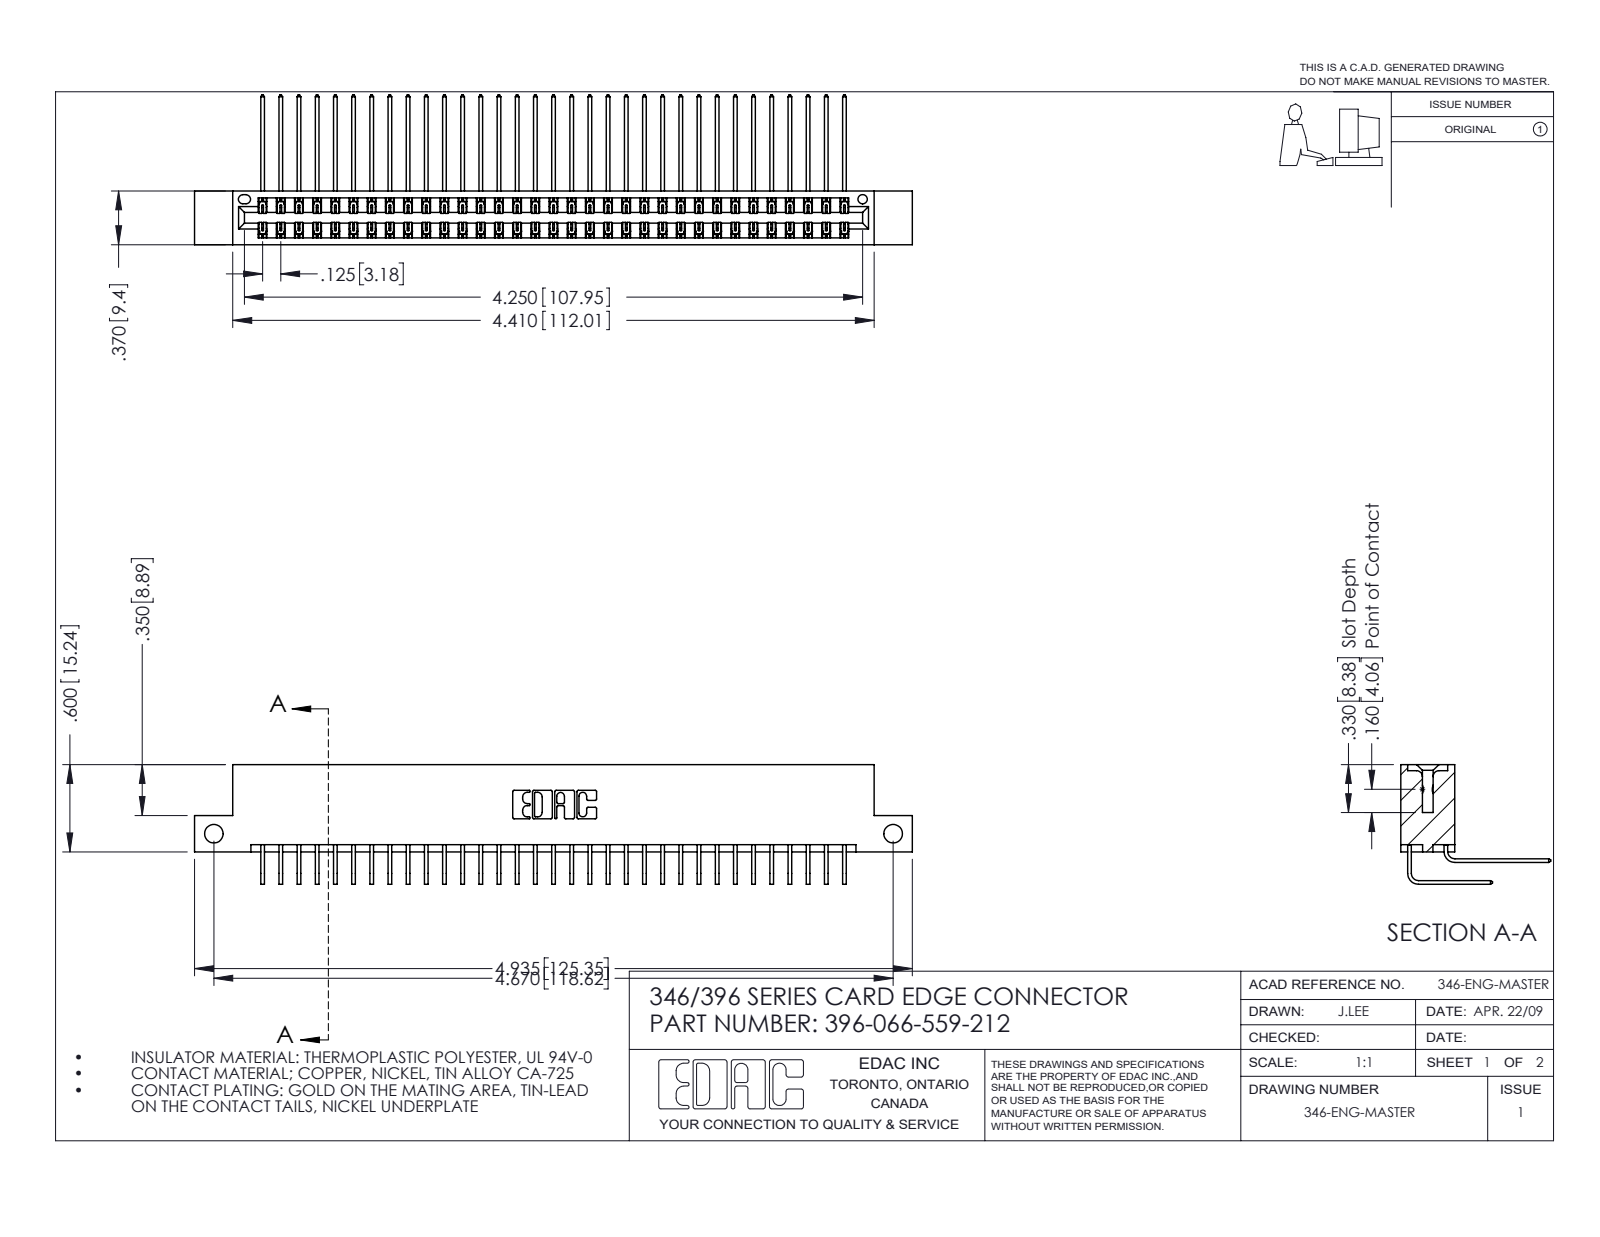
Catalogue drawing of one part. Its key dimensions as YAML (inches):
part_name: "345-292-001_558 559 Tail - 1; 345-292-001_559 Tail - 2; 346 Part_Flush Mounting Lugs - Side Mount; 396-066-559-212"
step_written_by: "SolidWorks 2016 (CONFIG_CONTROL_DESIGN)"
units: inches
bodies: {solids: 67, faces: 3686, planar: 2518, cylindrical: 1168, other: 0}
overall_size: [4.935, 1.03, 0.823]
volume: 0.76
surface_area: 28.92
round_holes:
  - {diameter: 0.128, count: 2}
  - {diameter: 0.064, count: 1}
partial_cylinders:
  - {radius: 0.006, count: 99}
  - {radius: 0.01, count: 22}
  - {radius: 0.007, count: 6}
  - {radius: 0.031, count: 6}
  - {radius: 0.026, count: 3}
  - {radius: 0.014, count: 2}
  - {radius: 0.022, count: 2}
  - {radius: 0.024, count: 2}
face_to_face_distances: [0.048, 0.322, 0.025, 0.25, 0.37, 0.072, 0.298, 0.275, 0.148, 0.222]
hole_center_spacings: [4.67]
